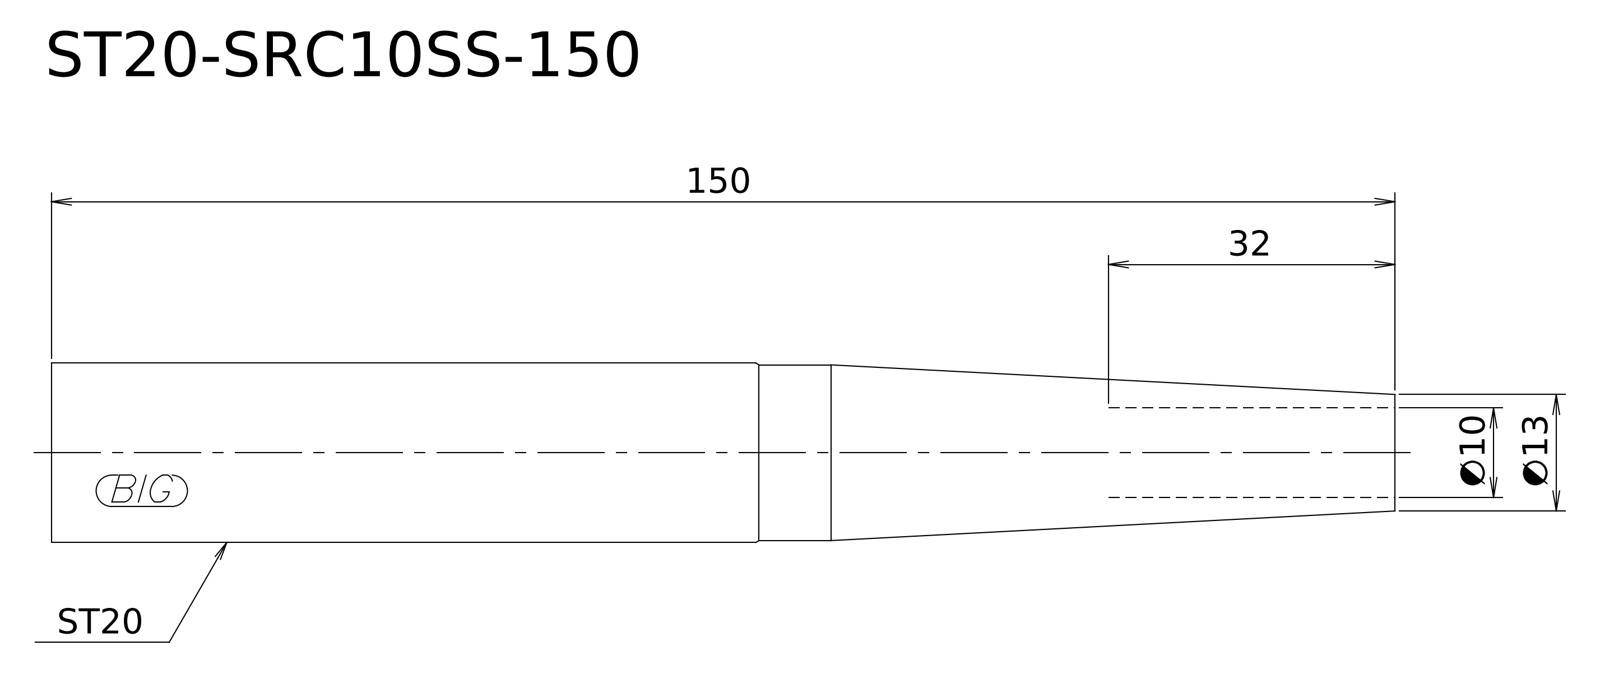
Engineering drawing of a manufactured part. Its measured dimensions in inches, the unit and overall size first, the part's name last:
Units: inches
Overall size (bounding box): 5.906 × 0.787 × 0.787
Round bosses / shafts (diameter × count): ⌀0.787 ×1, ⌀0.772 ×1
Main face-to-face distances: 5.906
Volume: 2.475 in³ · Surface area: 14.16 in²
Bodies: 1 solid, 6 faces (2 planar, 2 cylindrical, 2 other)
STEP written by: Kubotek KeyCreator V8.5.1 (14335) (CONFIG_CONTROL_DESIGN)
